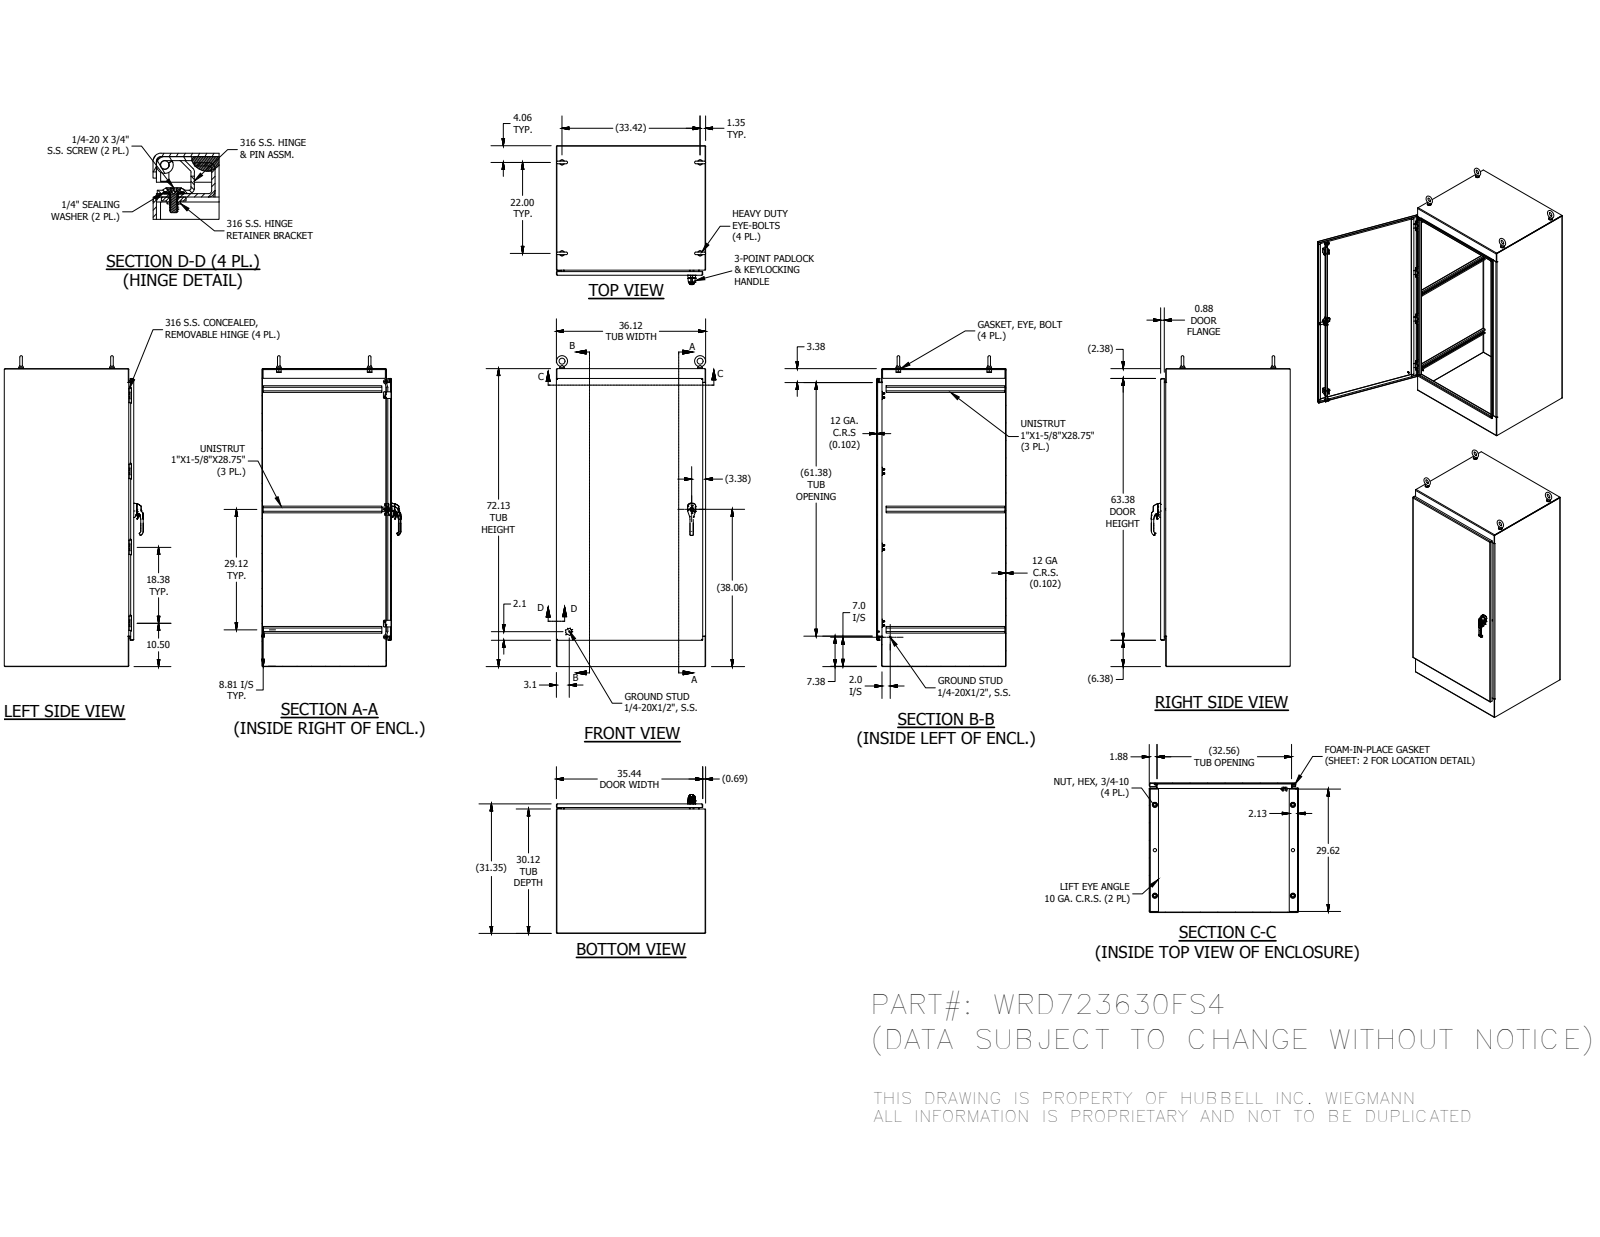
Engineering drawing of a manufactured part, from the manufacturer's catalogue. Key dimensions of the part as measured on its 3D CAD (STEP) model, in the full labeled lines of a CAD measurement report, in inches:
Part name (STEP PRODUCT): WRD723630FS4BLR; WRD3630FS4TOP; WRD3630FS4BTM; WRD7236FS4DR (+8 more)
STEP written by: Autodesk Inventor 2016 (AUTOMOTIVE_DESIGN)
Units: inches
Bodies: 91 solids, 3736 faces (1481 planar, 1241 cylindrical, 1014 other)
Overall size (bounding box): 75.248 × 36.127 × 33.616
Volume: 1 455 in³ · Surface area: 27 840 in²
Round holes (diameter × count): ⌀0.23 ×8, ⌀0.276 ×8, ⌀0.281 ×8, ⌀0.65 ×8, ⌀0.813 ×6, ⌀0.2 ×4, ⌀0.642 ×4, ⌀0.213 ×3, ⌀0.236 ×3, ⌀0.28 ×3, ⌀0.241 ×2, ⌀0.25 ×2
Round bosses / shafts (diameter × count): ⌀0.25 ×15, ⌀0.625 ×8, ⌀0.404 ×8, ⌀0.182 ×8, ⌀1.25 ×4, ⌀1.12 ×4, ⌀0.75 ×4, ⌀1 ×2
Partial cylindrical surfaces — rounded edges, fillets, slot ends (radius × count): R0.02 ×164, R0.012 ×86, R0.063 ×27, R0.01 ×24, R0.125 ×20, R0.019 ×19, R0.079 ×15, R0.05 ×14
Main face-to-face distances: 0.102, 31.245, 36.023, 31.143, 35.921, 31.347, 72.023, 36.125, 71.921, 72.125
Hole centre spacings: 0.492, 1, 11, 18.375, 35.185, 36.75, 0.256, 0.886
